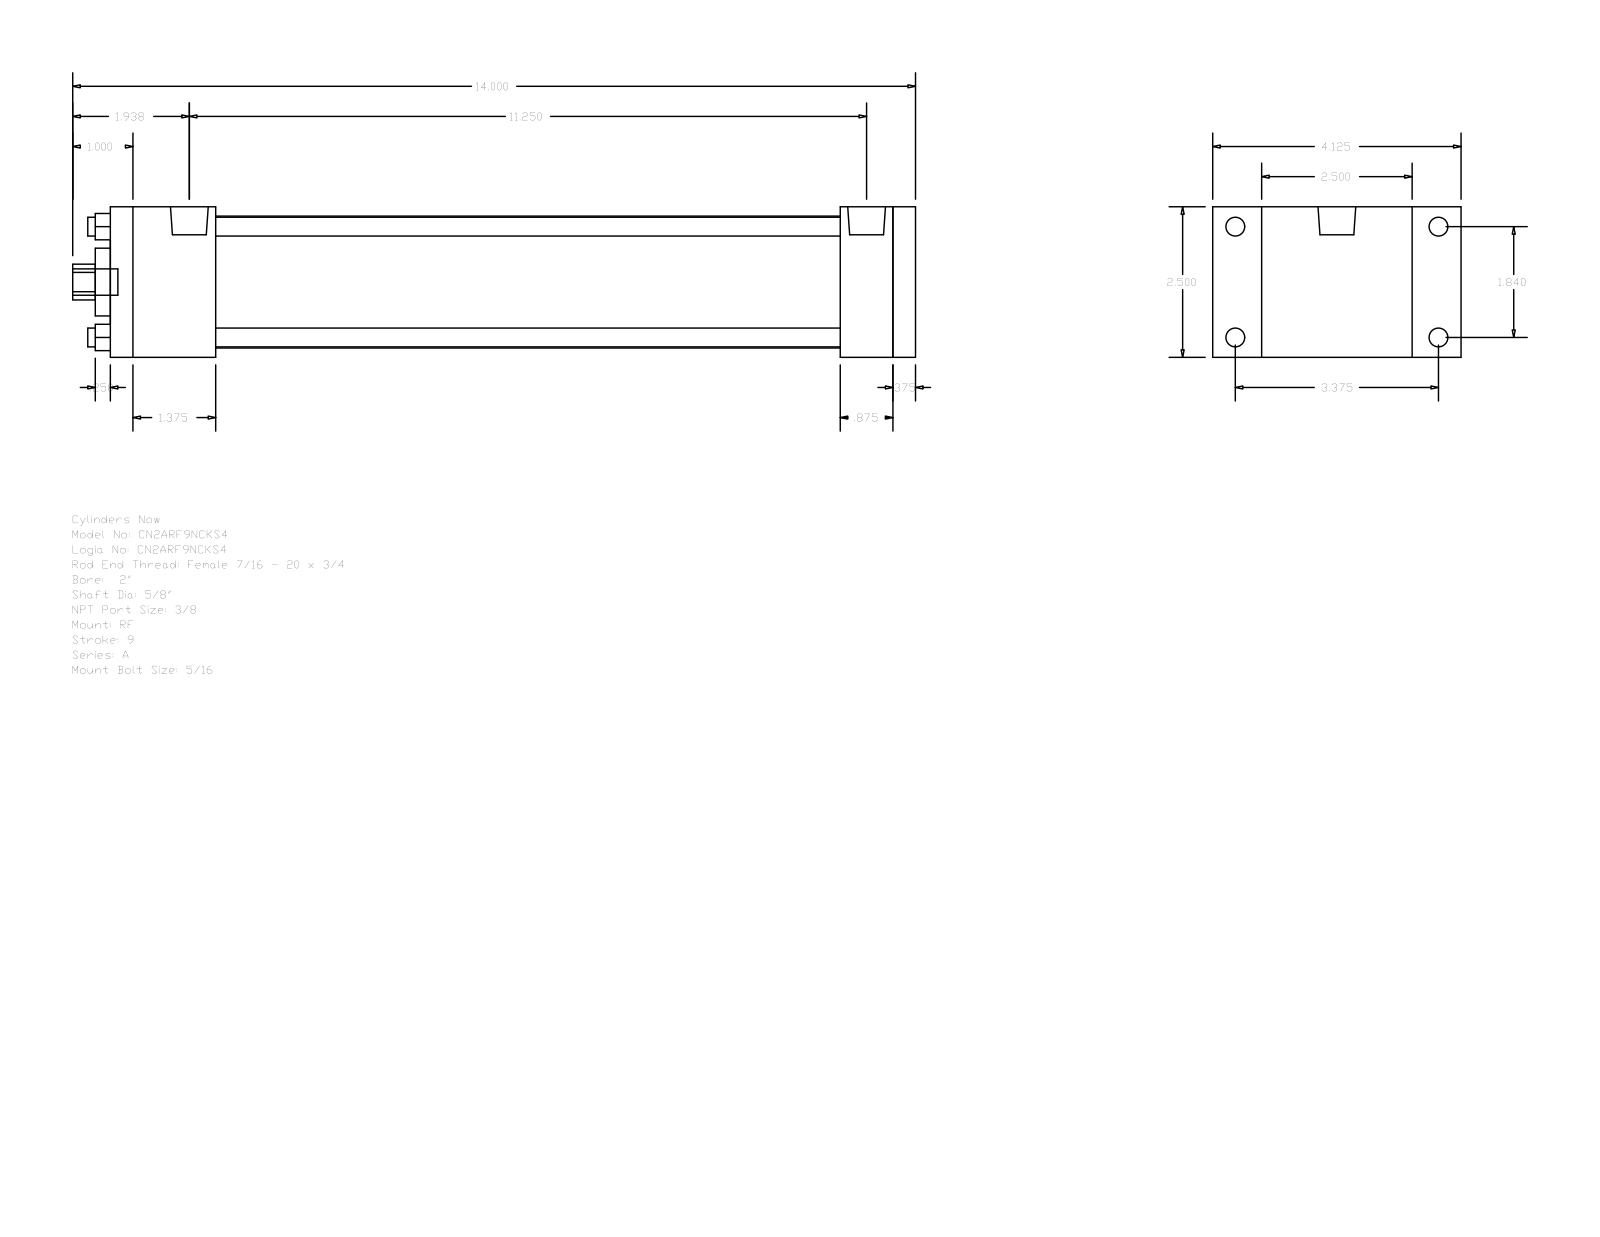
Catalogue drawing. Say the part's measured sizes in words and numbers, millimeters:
The part is named "A_RF__0200_0.625". Its 3-D file was written by "GSSL Pune (CONFIG_CONTROL_DESIGN)". It is 0 solids with 92 faces: 64 planar, 28 cylindrical and 0 other. Overall it measures 355.6 by 104.78 by 63.5 millimeters. Round holes: 4 of diameter 7.94, 1 of diameter 15.88, 1 of diameter 28.57, 1 of diameter 55.63. Round bosses or shafts: 4 of diameter 7.94, 4 of diameter 5.56, 2 of diameter 15.93, 1 of diameter 11.11. Partial cylindrical surfaces (rounded edges, fillets, slot ends): 1 of radius 7.54. The main face-to-face distances are 63.5, 339.72, 9.53, 330.19, 44.45, 285.74, 295.27, 307.97, 263.52, 22.22. The hole center spacings are 33.05, 46.74, 66.1.
